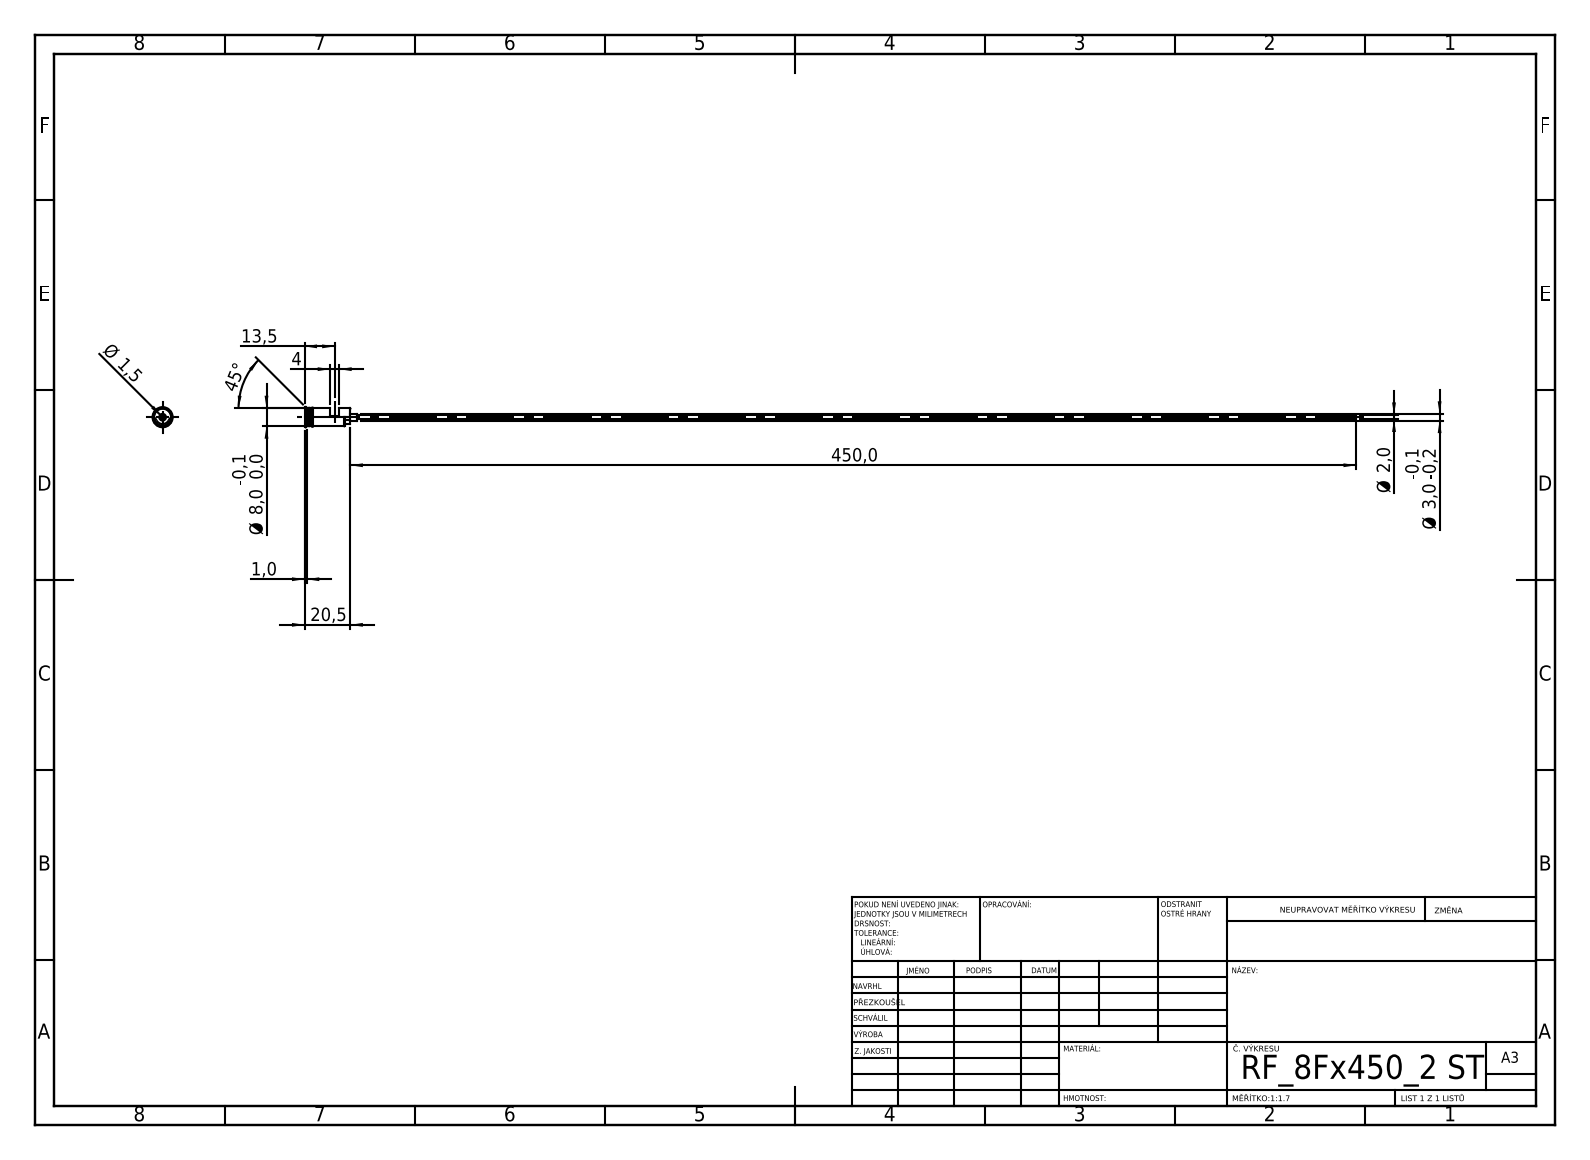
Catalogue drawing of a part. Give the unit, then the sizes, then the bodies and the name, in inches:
Units: inches
Overall size (bounding box): 18.524 × 0.354 × 0.354
Round holes (diameter × count): ⌀0.059 ×1
Round bosses / shafts (diameter × count): ⌀0.354 ×1, ⌀0.315 ×1, ⌀0.307 ×1, ⌀0.118 ×1, ⌀0.079 ×1
Partial cylindrical surfaces — rounded edges, fillets, slot ends (radius × count): R0.118 ×2, R0.12 ×1
Main face-to-face distances: 0.157, 0.807, 0.354, 0.453, 0.197, 0.61, 0.098, 0.728, 0.531, 0.374
Volume: 0.093 in³ · Surface area: 8.816 in²
Bodies: 1 solid, 55 faces (24 planar, 19 cylindrical, 12 other)
STEP written by: SolidWorks 2019 (CONFIG_CONTROL_DESIGN)
